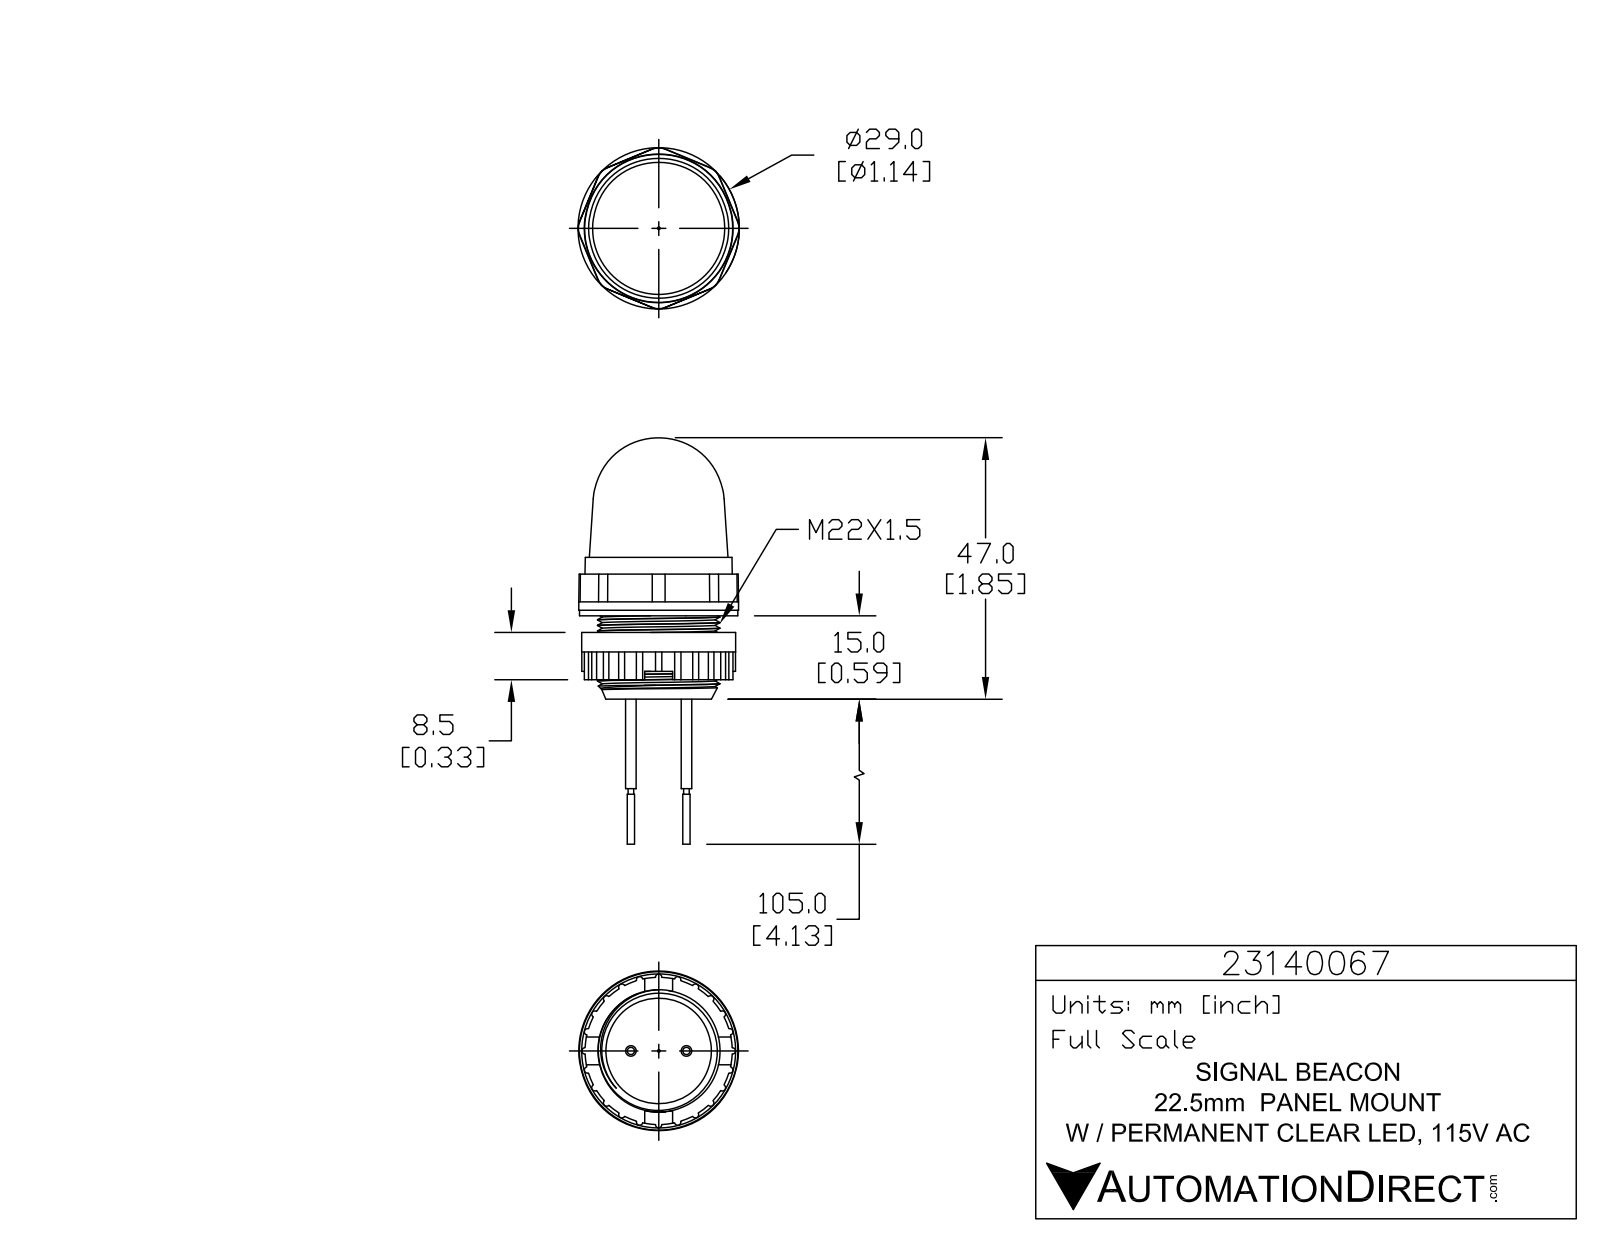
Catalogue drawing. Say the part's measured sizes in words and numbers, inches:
The part is named "23140067". Its 3-D file was written by "SolidWorks 2017 (AUTOMOTIVE_DESIGN)". It is 1 solid with 934 faces: 568 planar, 269 cylindrical and 97 other. Overall it measures 2.82 by 1.131 by 1.131 inches. Its volume is 1.255 cubic inches and its surface area 12.16 square inches. Round holes: 3 of diameter 0.02. Round bosses or shafts: 3 of diameter 0.113, 3 of diameter 0.028, 2 of diameter 0.075, 2 of diameter 0.051, 2 of diameter 0.039, 1 of diameter 1.131, 1 of diameter 1.122, 1 of diameter 1.091. Partial cylindrical surfaces (rounded edges, fillets, slot ends): 24 of radius 0.023, 8 of radius 0.118, 6 of radius 0.004, 6 of radius 0.004, 6 of radius 0.004, 6 of radius 0.065, 3 of radius 0.005, 3 of radius 0.007. The main face-to-face distances are 0.551, 0.118, 0.433, 0.098, 0.335, 0.453, 0.492, 0.413, 0.295, 0.197.
